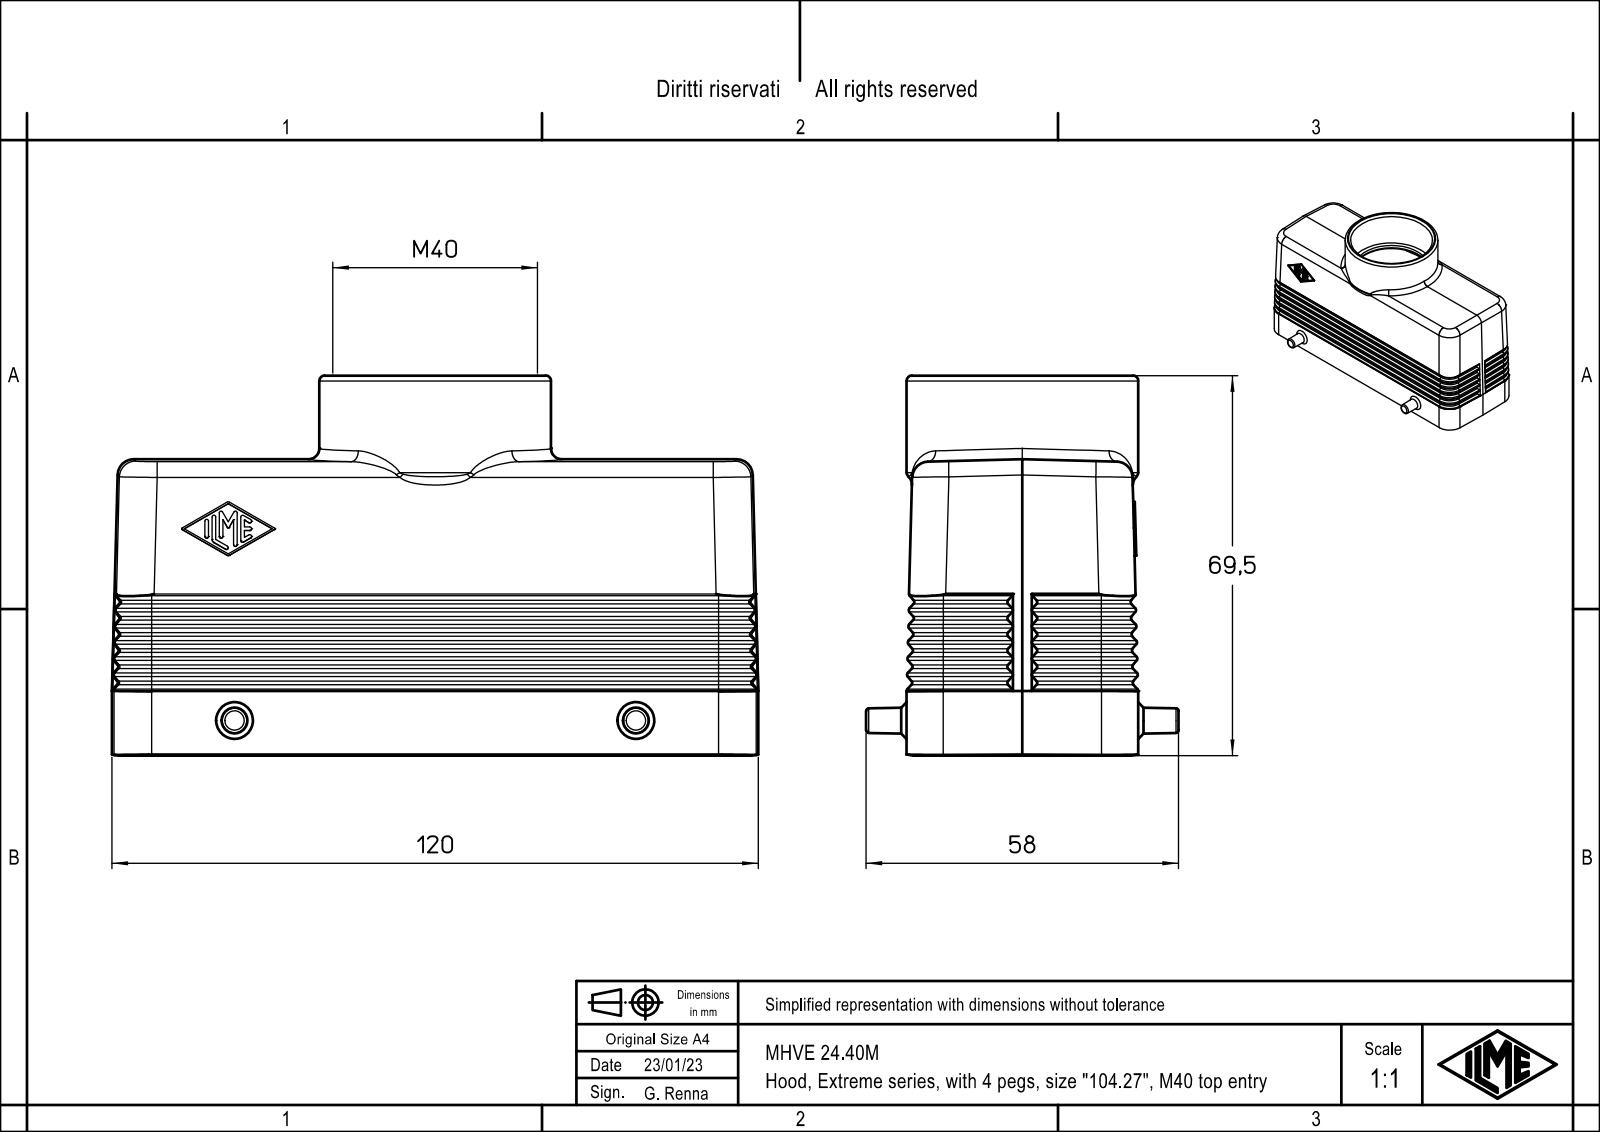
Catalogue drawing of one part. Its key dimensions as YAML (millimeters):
part_name: "MHVE_24.40M"
step_written_by: "PTC Creo Elements/Direct Modeling 19.0E 27-Jun-2016 (C) Parametric Technology GmbH (AUTOMOTIVE_DESIGN)"
units: millimeters
bodies: {solids: 1, faces: 409, planar: 221, cylindrical: 116, other: 72}
overall_size: [120, 68, 55]
volume: 74198
surface_area: 46748
round_holes:
  - {diameter: 2.46, count: 4}
  - {diameter: 4, count: 4}
  - {diameter: 34.84, count: 1}
  - {diameter: 40, count: 1}
round_bosses_or_shafts:
  - {diameter: 5, count: 2}
  - {diameter: 43, count: 1}
partial_cylinders:
  - {radius: 0.25, count: 14}
  - {radius: 3, count: 8}
  - {radius: 2, count: 4}
  - {radius: 5.3, count: 4}
  - {radius: 6, count: 4}
  - {radius: 1.5, count: 1}
  - {radius: 19, count: 1}
face_to_face_distances: [3, 40, 37, 43, 11.5, 8.5, 1.77, 117, 5.3, 20]
hole_center_spacings: [53.72, 27, 104, 107.45]
